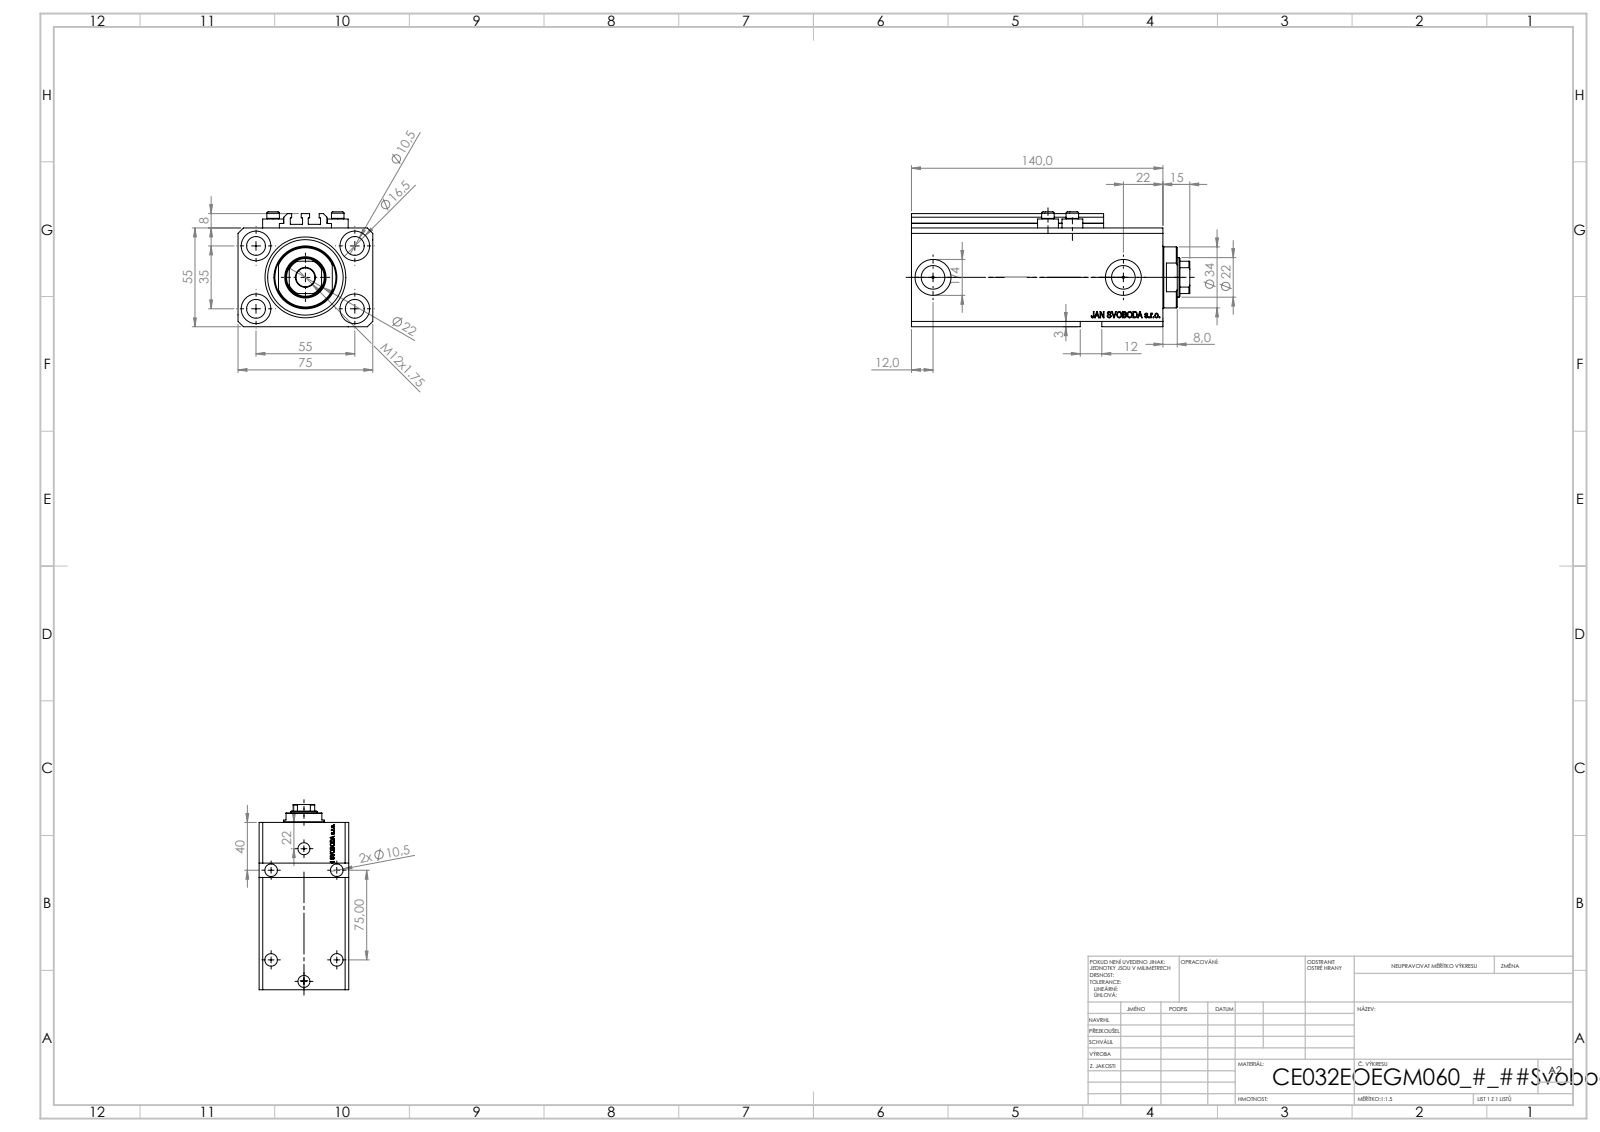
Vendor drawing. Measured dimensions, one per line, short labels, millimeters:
name: V250CE_VC_E; V250CE_E_Body; ALLEN BOLT V250CE; V250CE_C_VCP
written by: SolidWorks 2019 (CONFIG_CONTROL_DESIGN)
unit: mm
bodies: 8 solids, 1084 faces (514 planar, 146 cylindrical, 424 other)
size: 155 × 75 × 64
volume: 485 219 mm³; area: 115 303 mm²
holes: 9× ⌀10.5, 4× ⌀1.25, 4× ⌀4, 4× ⌀16.5, 2× ⌀10, 2× ⌀13.16, 2× ⌀20, 1× ⌀22, 1× ⌀32, 1× ⌀45
bosses: 4× ⌀11.6, 4× ⌀7, 1× ⌀34
rounds: 10× R0.2, 1× R10.5
face distances: 55, 75, 15, 140, 125, 3, 9.9, 57, 115.1, 130.1
hole spacings: 32.6, 32.87, 55, 96.98, 13.6, 14.09, 25.81, 32.58
